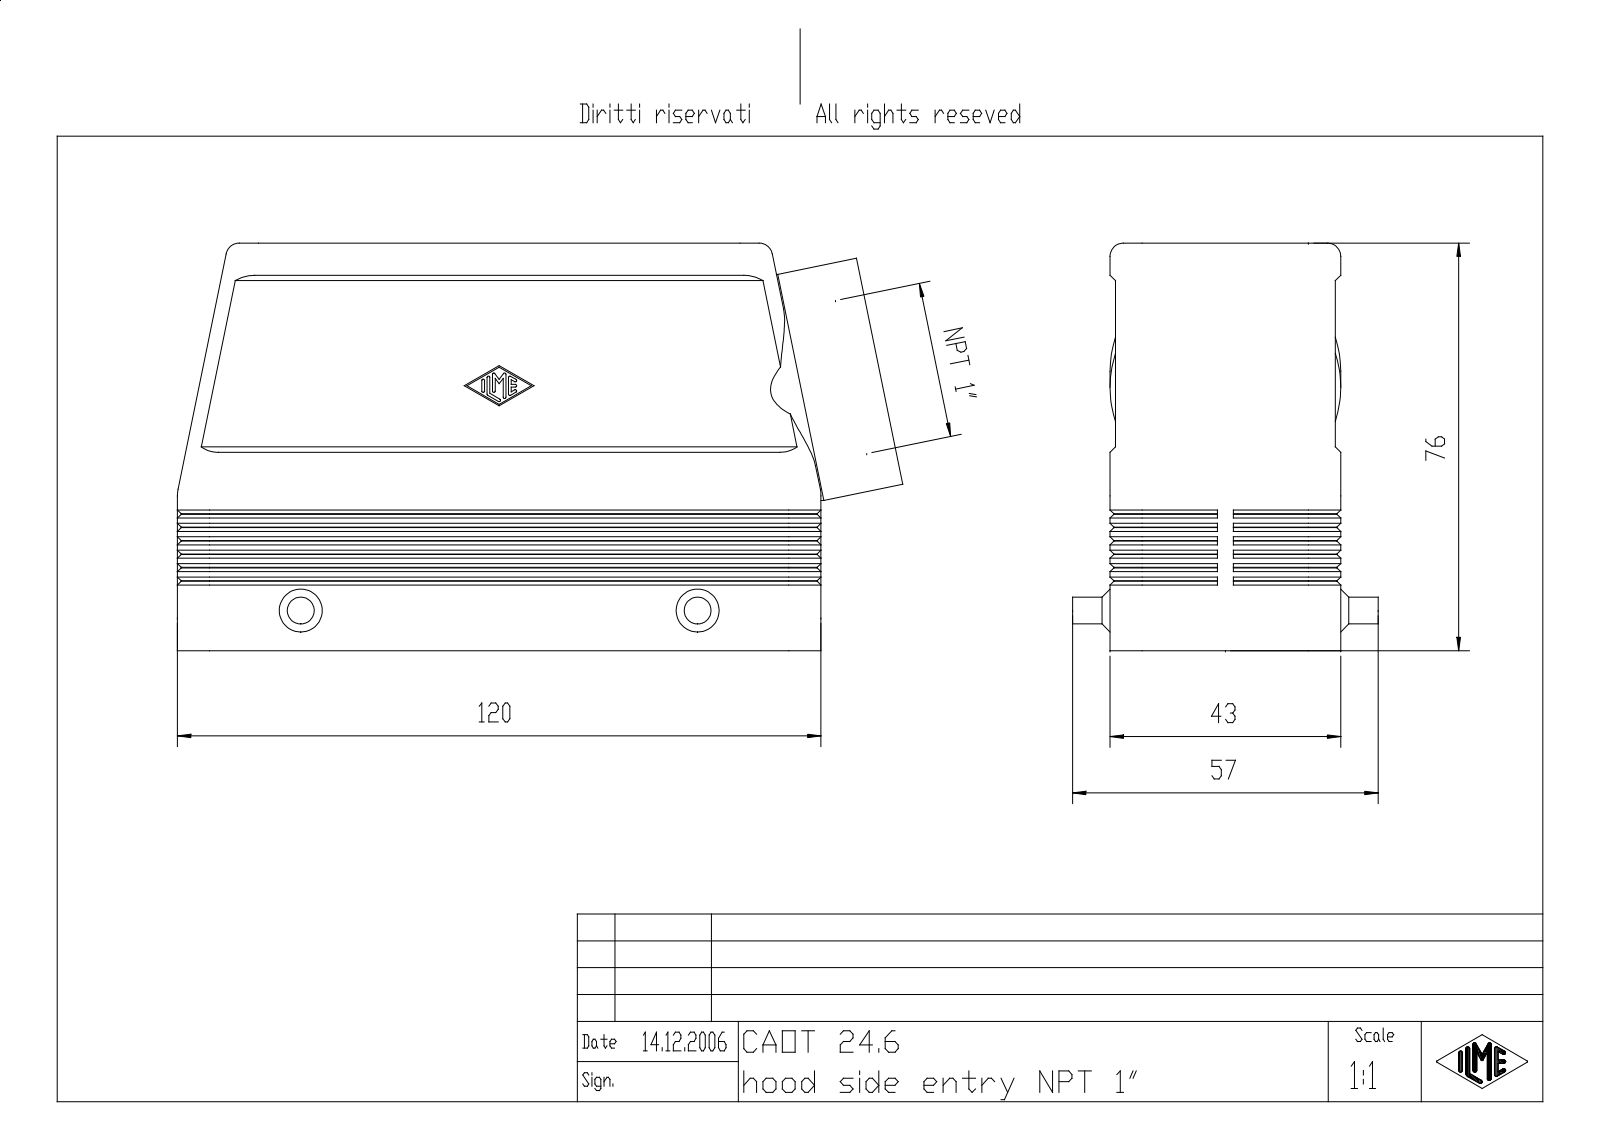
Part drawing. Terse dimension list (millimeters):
name: MSBO8691
written by: Creo Elements/Direct Modeling 18.0B 02-Dec-2011 (C) Parametric Technology GmbH (AUTOMOTIVE_DESIGN)
unit: mm
bodies: 1 solid, 421 faces (228 planar, 115 cylindrical, 78 other)
size: 135.24 × 76 × 57
volume: 94 311 mm³; area: 57 644 mm²
holes: 4× ⌀4, 3× ⌀2.46, 1× ⌀2.46
bosses: 2× ⌀5, 1× ⌀43
rounds: 14× R0.25, 12× R6, 4× R2, 4× R2.5, 4× R3, 4× R5.3
face distances: 3, 37, 2, 40, 39, 1, 42, 43, 41, 1.77
hole spacings: 27, 104, 107.45
